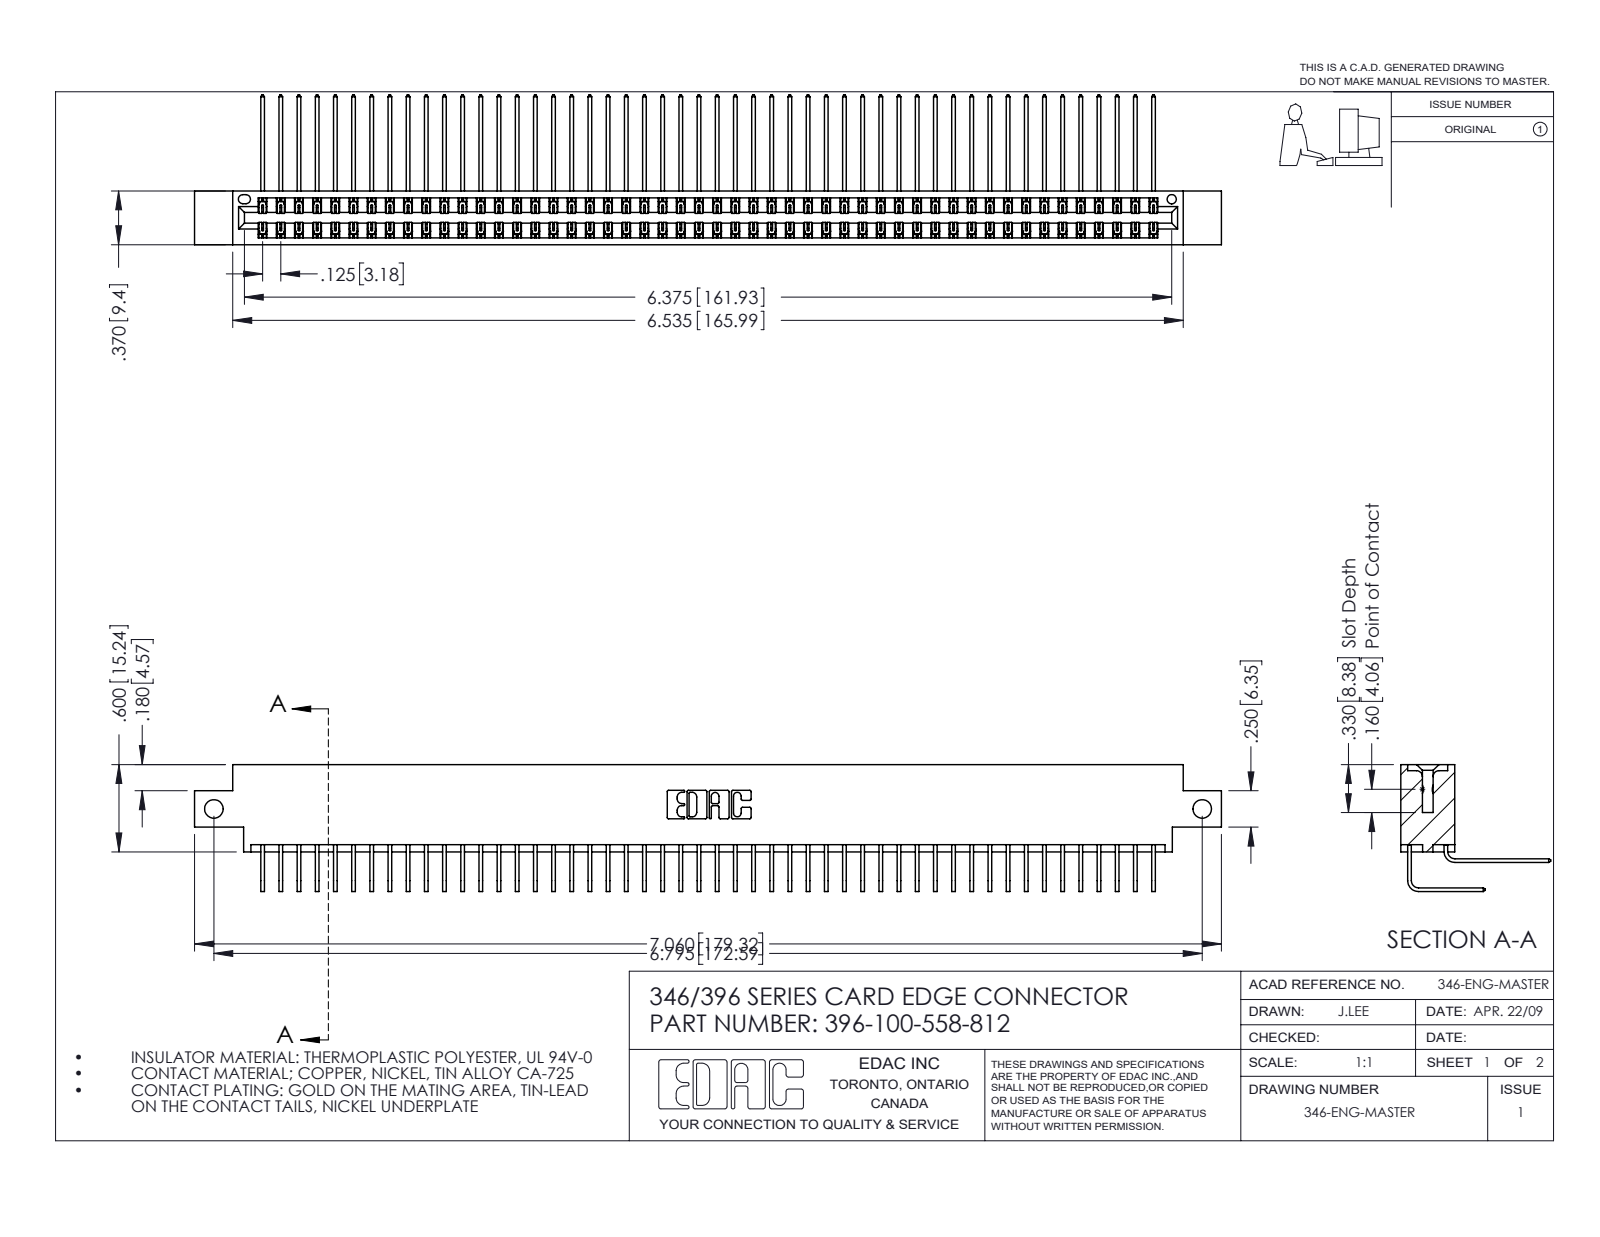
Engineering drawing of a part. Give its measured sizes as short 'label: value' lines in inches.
name: 345-292-001_558 Tail - 2; 346 Part_0.170 Offset - Side Mount; 345-292-001_558 559 Tail - 1; 396-100-558-812
written by: SolidWorks 2016 (CONFIG_CONTROL_DESIGN)
unit: in
bodies: 101 solids, 5526 faces (3780 planar, 1746 cylindrical, 0 other)
size: 7.06 × 1.03 × 0.873
volume: 1.091 in³; area: 42.65 in²
holes: 2× ⌀0.128, 1× ⌀0.064
rounds: 150× R0.006, 22× R0.01, 6× R0.007, 6× R0.031, 3× R0.026, 2× R0.014, 2× R0.022, 2× R0.024
face distances: 0.322, 0.048, 0.025, 0.37, 0.25, 0.298, 0.072, 0.275, 0.148, 0.222
hole spacings: 6.795
